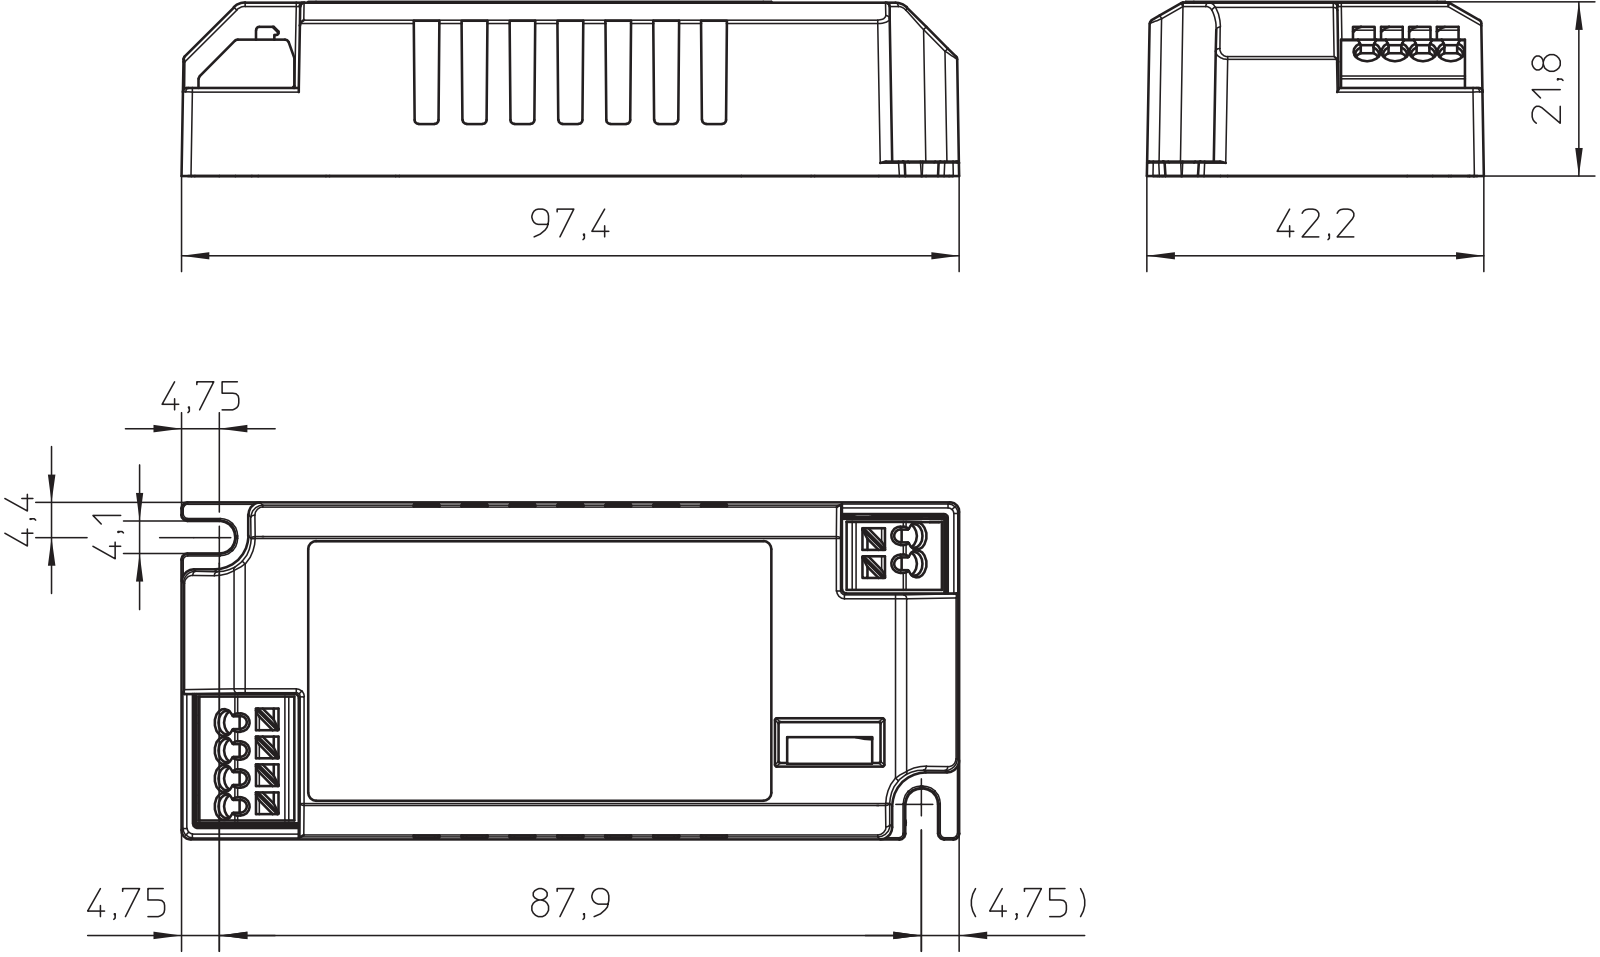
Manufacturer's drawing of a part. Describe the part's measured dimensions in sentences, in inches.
The part is named "casing_top; PCB; clamp1; clamp2 (+3 more)". Its 3-D file was written by "PTC Creo Elements/Direct Modeling 19.0E 27-Jun-2016 (C) Parametric Technology GmbH (AUTOMOTIVE_DESIGN)". It is 6 solids with 1925 faces: 872 planar, 526 cylindrical and 527 other. Overall it measures 4.573 by 1.661 by 1.102 inches. Its volume is 1.677 cubic inches and its surface area 61.82 square inches. Round holes: 32 of diameter 0.039, 8 of diameter 0.043, 6 of diameter 0.118, 4 of diameter 0.045, 1 of diameter 0.083. Round bosses or shafts: 1 of diameter 0.689, 1 of diameter 0.016. Partial cylindrical surfaces (rounded edges, fillets, slot ends): 105 of radius 0.008, 95 of radius 0.02, 14 of radius 0.006, 14 of radius 0.012, 12 of radius 0.004, 11 of radius 0.016, 10 of radius 0.035, 9 of radius 0.039. The main face-to-face distances are 0.047, 0.219, 0.065, 0.154, 0.106, 0.172, 0.049, 0.805, 0.758, 0.652. The hole center spacings are 0.394, 0.138, 0.098, 0.197, 0.276, 0.289, 0.337, 0.557.
